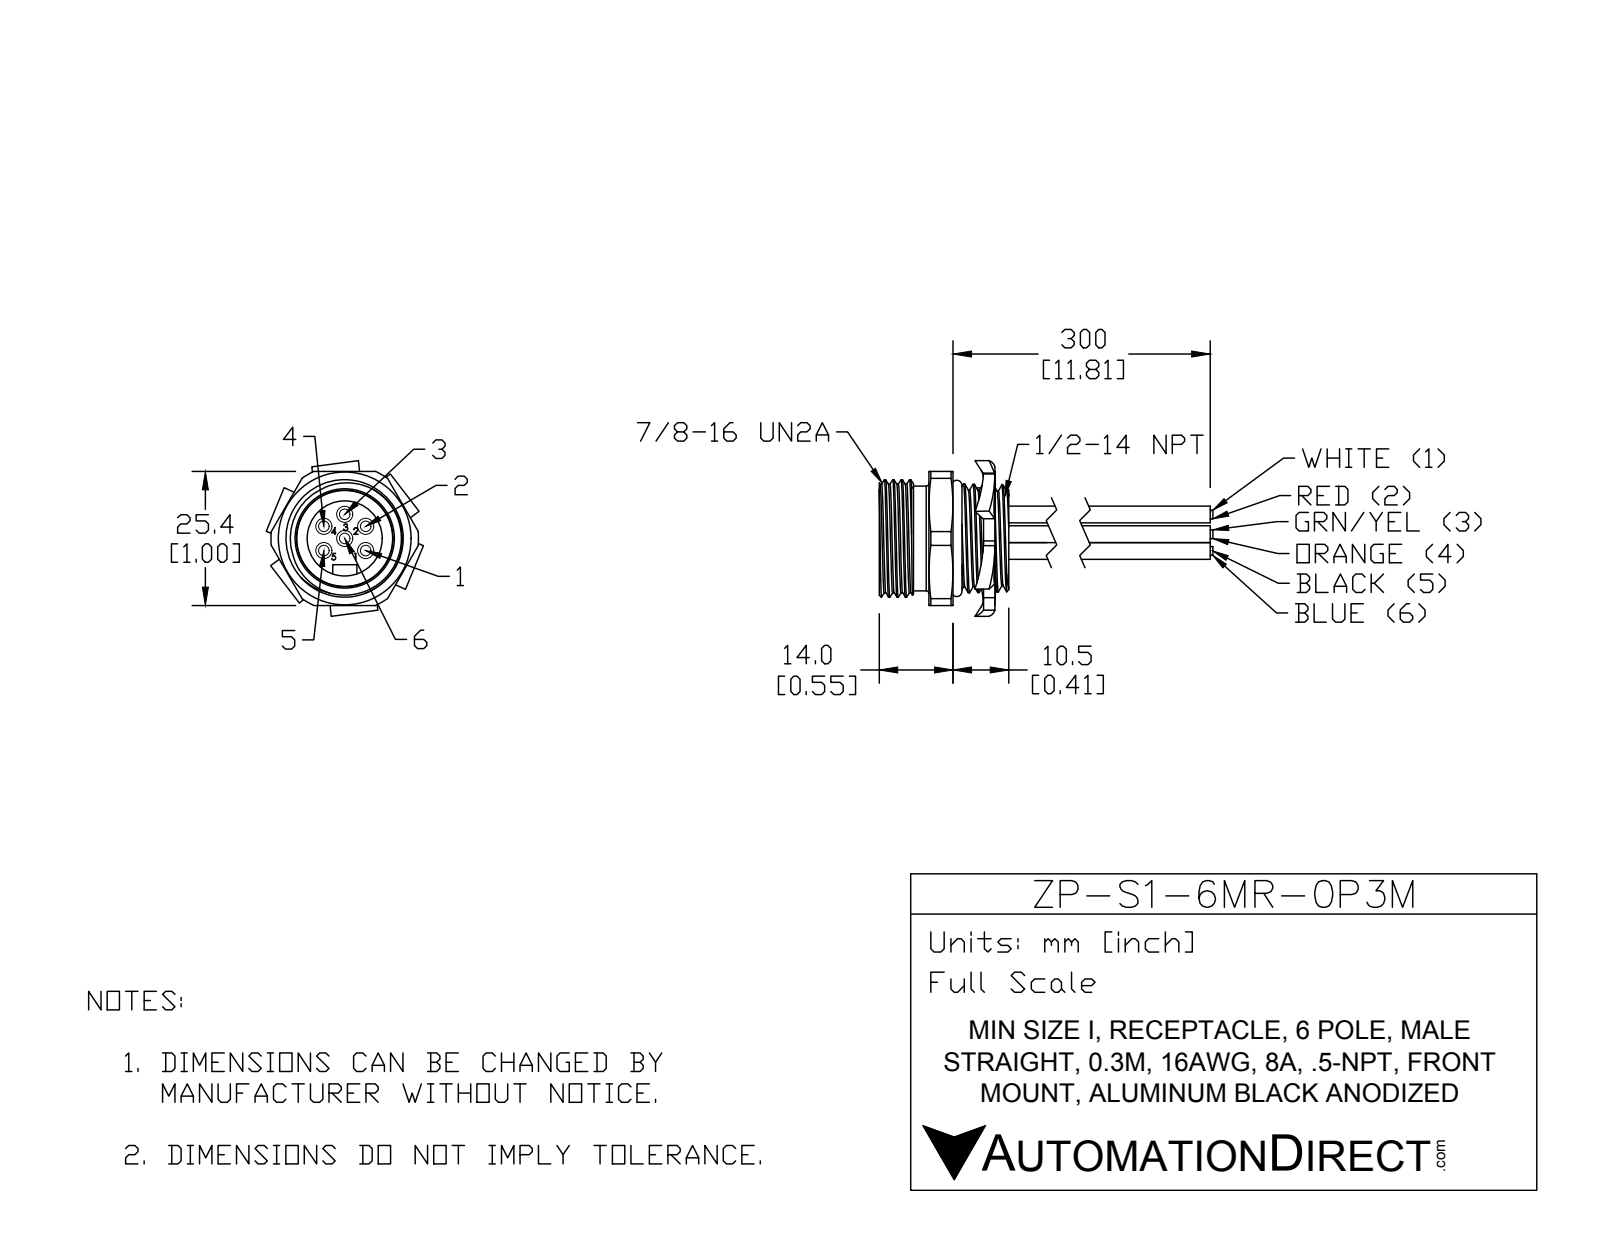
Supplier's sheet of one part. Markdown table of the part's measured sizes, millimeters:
| quantity | value |
| --- | --- |
| part name | MIN-6MR-ZZ |
| STEP written by | SolidWorks 2015 (AUTOMOTIVE_DESIGN) |
| units | millimeters |
| bodies | 1 solid, 280 faces (89 planar, 86 cylindrical, 105 other) |
| overall size | 49.91 × 29.77 × 29.48 |
| volume | 9 556 mm³ |
| surface area | 7 233 mm² |
| round holes (diameter × count) | 14.22 × 1, 18.29 × 1, 19.61 × 1 |
| round bosses / shafts (diameter × count) | 3.18 × 6, 3.05 × 6, 2 × 6, 25.37 × 1, 22.22 × 1, 20.6 × 1, 19.81 × 1, 18.14 × 1 |
| partial cylindrical surfaces (radius × count) | 2.29 × 1, 13.97 × 1 |
| main face-to-face distances | 25.4, 6.35, 12.37, 15.11, 4.57, 10.54, 1.45, 6.02, 16.56, 7.8 |
